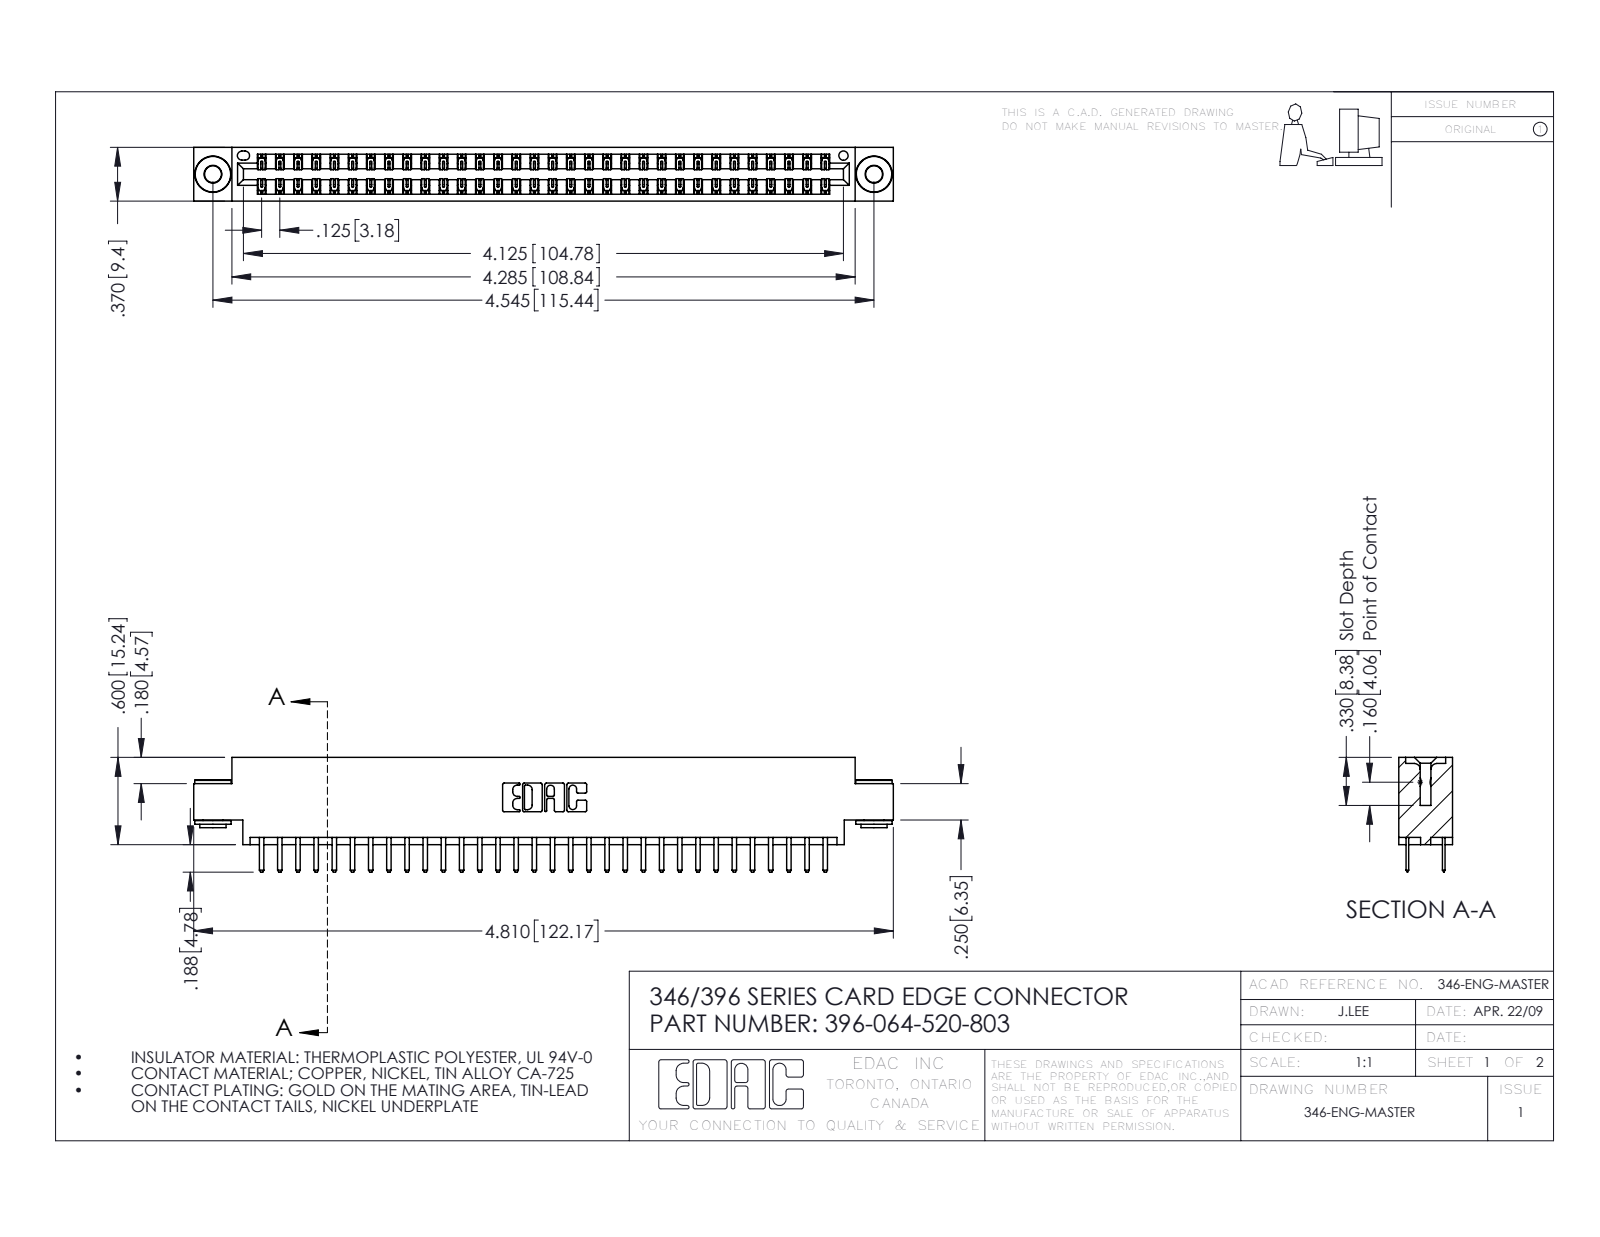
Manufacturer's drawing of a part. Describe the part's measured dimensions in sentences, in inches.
The part is named "345-292-001_345-293-120; 346 Part_0.170 Offset - 0.156 Dia-TH; 345-250-002_345-250-002-102; 396-064-520-803". Its 3-D file was written by "SolidWorks 2016 (CONFIG_CONTROL_DESIGN)". It is 67 solids with 3748 faces: 2458 planar, 1282 cylindrical and 8 other. Overall it measures 4.81 by 0.788 by 0.37 inches. Its volume is 0.712 cubic inches and its surface area 25.13 square inches. Round holes: 2 of diameter 0.116, 2 of diameter 0.156, 1 of diameter 0.064. Round bosses or shafts: 2 of diameter 0.25, 2 of diameter 0.18, 2 of diameter 0.136. Partial cylindrical surfaces (rounded edges, fillets, slot ends): 96 of radius 0.006, 68 of radius 0.01, 22 of radius 0.01, 6 of radius 0.007, 6 of radius 0.031, 3 of radius 0.026, 2 of radius 0.014, 2 of radius 0.022. The main face-to-face distances are 0.048, 0.322, 0.37, 0.25, 0.025, 0.275, 0.072, 0.298, 0.148, 0.222. The hole center spacings are 0.246, 4.337, 4.545.
